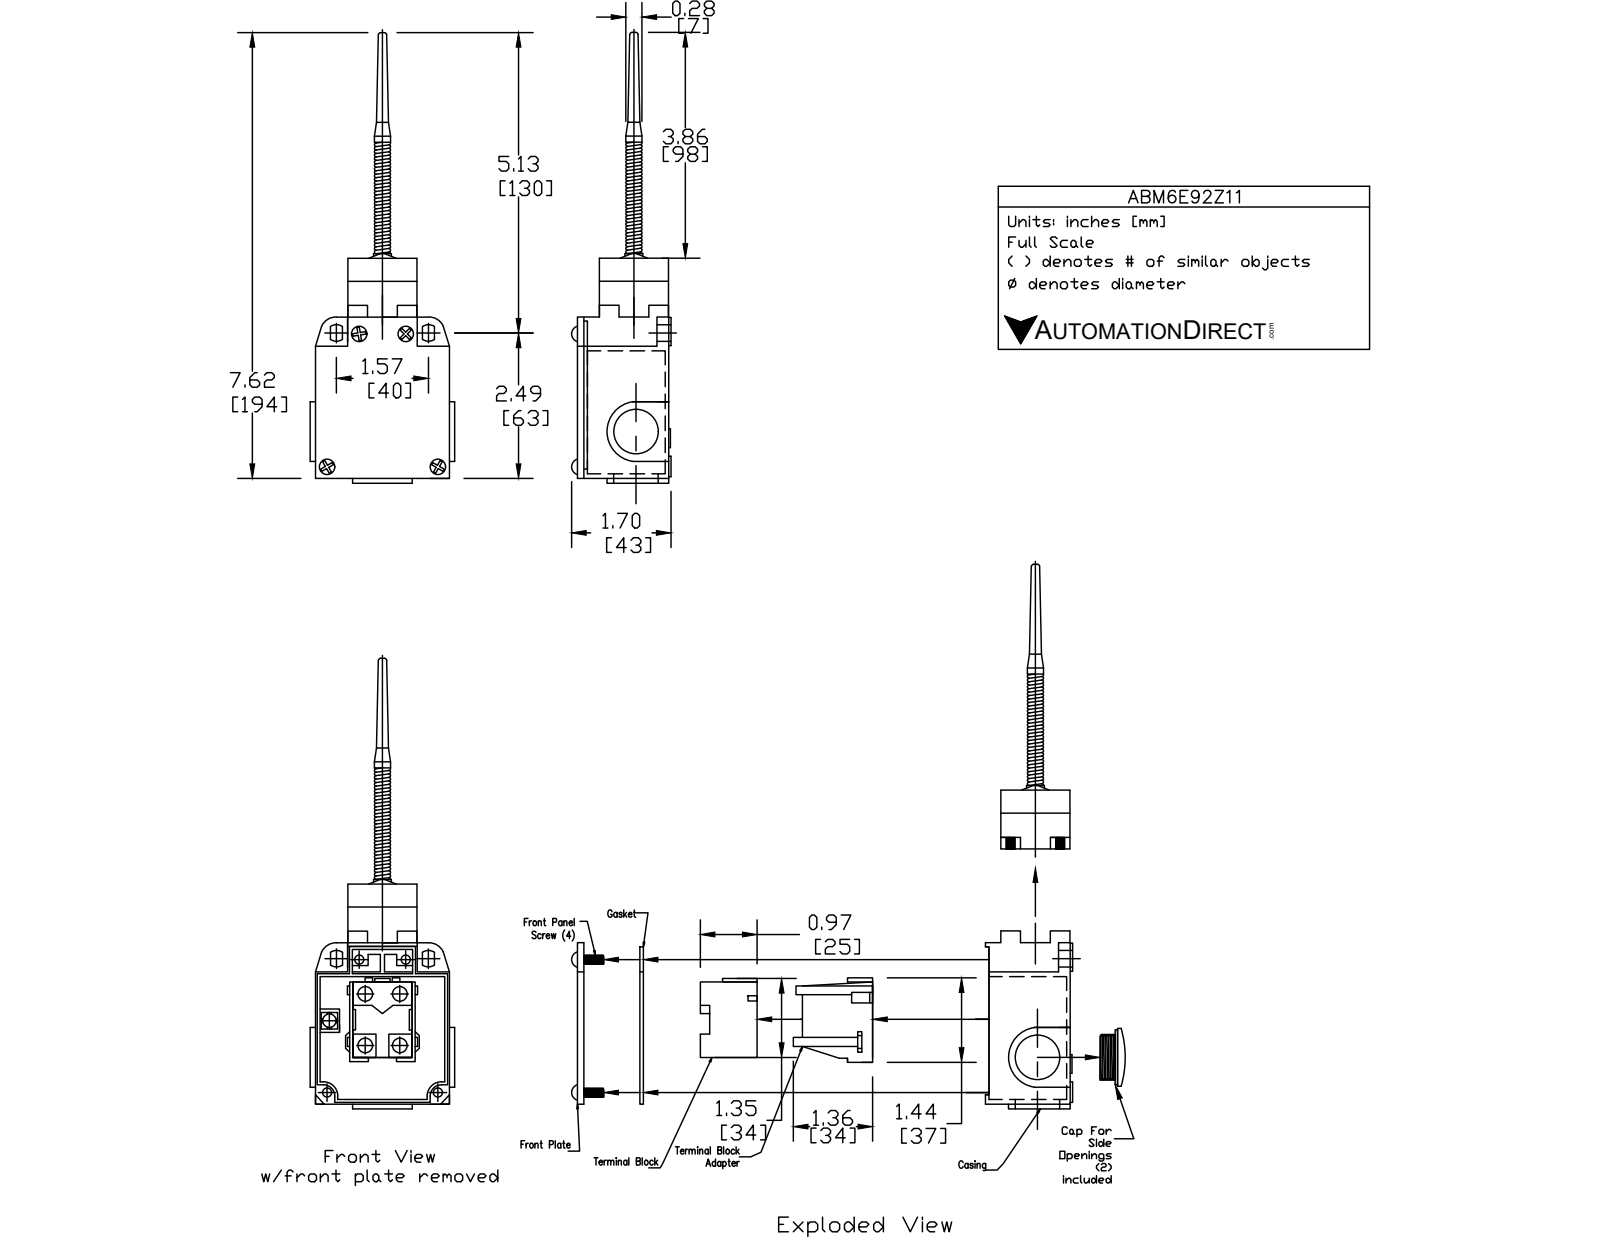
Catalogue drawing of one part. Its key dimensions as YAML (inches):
part_name: "ABM6E92Z11"
step_written_by: "SolidWorks 2017 (AUTOMOTIVE_DESIGN)"
units: inches
bodies: {solids: 3, faces: 222, planar: 88, cylindrical: 88, other: 46}
overall_size: [7.61, 2.441, 1.705]
volume: 10.24
surface_area: 41.29
round_holes:
  - {diameter: 0.669, count: 2}
  - {diameter: 0.748, count: 2}
  - {diameter: 0.807, count: 1}
round_bosses_or_shafts:
  - {diameter: 0.276, count: 8}
  - {diameter: 0.472, count: 2}
  - {diameter: 0.354, count: 2}
  - {diameter: 0.748, count: 1}
  - {diameter: 0.461, count: 1}
  - {diameter: 0.268, count: 1}
partial_cylinders:
  - {radius: 0.059, count: 12}
  - {radius: 0.02, count: 4}
  - {radius: 0.024, count: 4}
  - {radius: 0.144, count: 2}
  - {radius: 0.256, count: 2}
  - {radius: 0.512, count: 2}
  - {radius: 0.453, count: 1}
  - {radius: 0.472, count: 1}
face_to_face_distances: [1.555, 1.732, 0.551, 2.283, 1.181, 0.079, 2.756, 0.236, 0.512, 0.63]
hole_center_spacings: [0.039]
